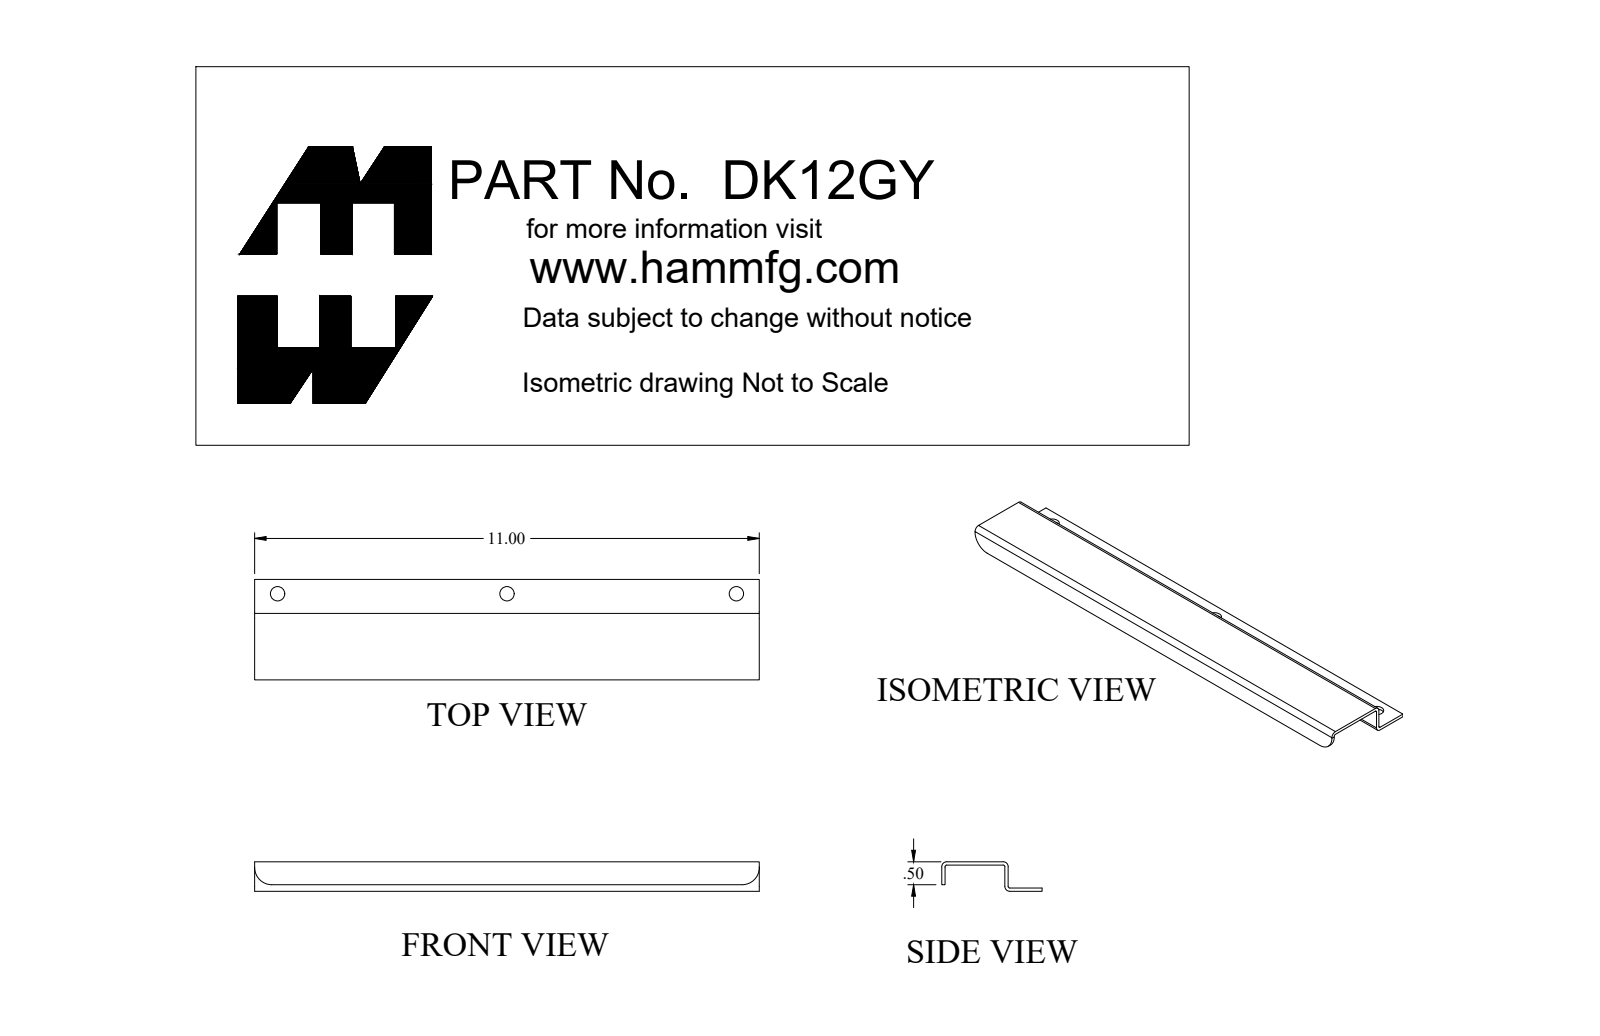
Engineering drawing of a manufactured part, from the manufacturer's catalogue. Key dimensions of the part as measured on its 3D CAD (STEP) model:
Part name (STEP PRODUCT): DK12GY_Default
STEP written by: SolidWorks 2018 (CONFIG_CONTROL_DESIGN)
Units: inches
Bodies: 2 solids, 32 faces (18 planar, 14 cylindrical, 0 other)
Overall size (bounding box): 11 × 2.188 × 0.707
Volume: 2.95 in³ · Surface area: 87.71 in²
Round holes (diameter × count): ⌀0.313 ×3
Partial cylindrical surfaces — rounded edges, fillets, slot ends (radius × count): R0.036 ×3, R0.108 ×3, R0.375 ×2
Main face-to-face distances: 0.072, 0.572, 0.644, 1.376, 0.5, 0.063, 0.635, 0.707, 0.135, 1.448
Hole centre spacings: 5, 10
